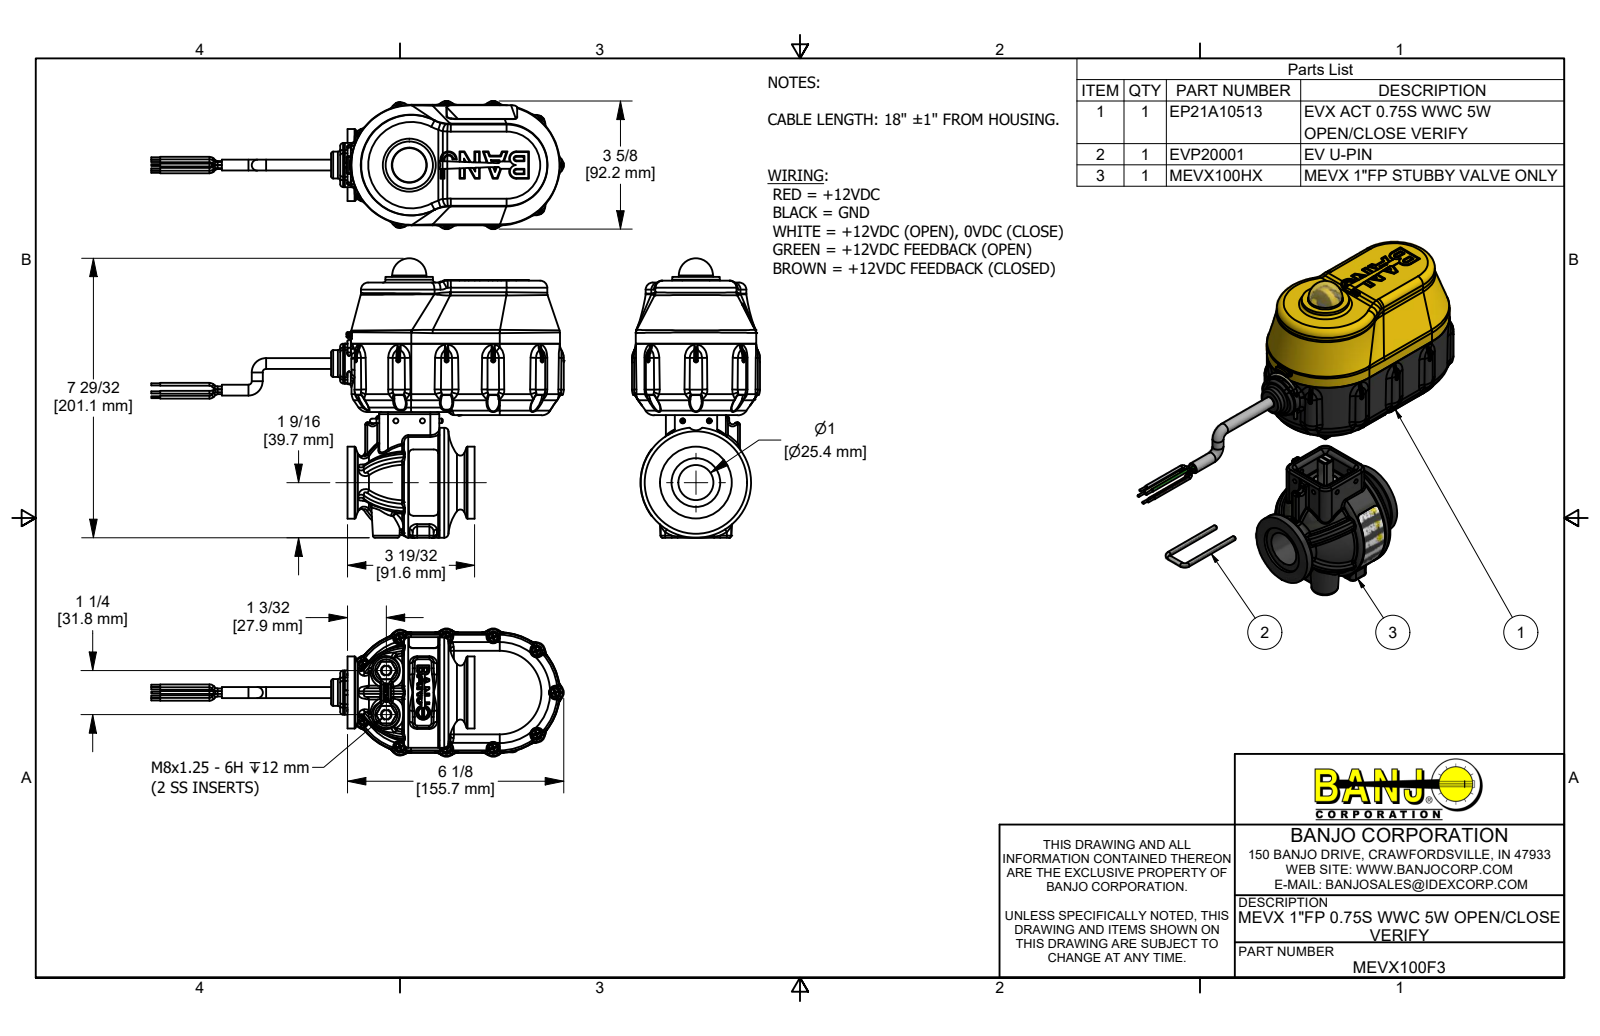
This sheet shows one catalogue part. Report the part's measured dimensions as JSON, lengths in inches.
{"part_name": "MEVX100F3; EP21A10513; EP10513; EP10310 (+8 more)", "step_written_by": "Autodesk Inventor 2019 (AUTOMOTIVE_DESIGN)", "units": "inches", "bodies": {"solids": 84, "faces": 11019, "planar": 3000, "cylindrical": 3129, "other": 4890}, "overall_size": [11.685, 7.916, 3.63], "volume_in3": 45.46, "surface_area_in2": 538.7, "round_holes": [[0.095, 11], [0.15, 11], [0.08, 7], [0.135, 5], [0.107, 4], [0.126, 4], [0.136, 4], [0.148, 4], [0.15, 4], [0.17, 4], [0.105, 2], [0.118, 2]], "round_bosses_or_shafts": [[0.08, 25], [0.25, 17], [0.14, 11], [0.108, 11], [0.085, 11], [0.058, 10], [0.27, 4], [0.219, 4]], "partial_cylinders_radius": [[0.013, 180], [0.04, 145], [0.01, 92], [0.02, 71], [0.005, 54], [0.06, 46], [0.03, 30], [0.08, 28]], "face_to_face_distances": [0.1, 2.565, 0.211, 0.06, 0.151, 1.896, 1.685, 1.836, 2.465, 0.78], "hole_center_spacings": [1.79, 1.283, 2.656, 1.513, 1.662, 2.69, 2.849, 3.789]}
